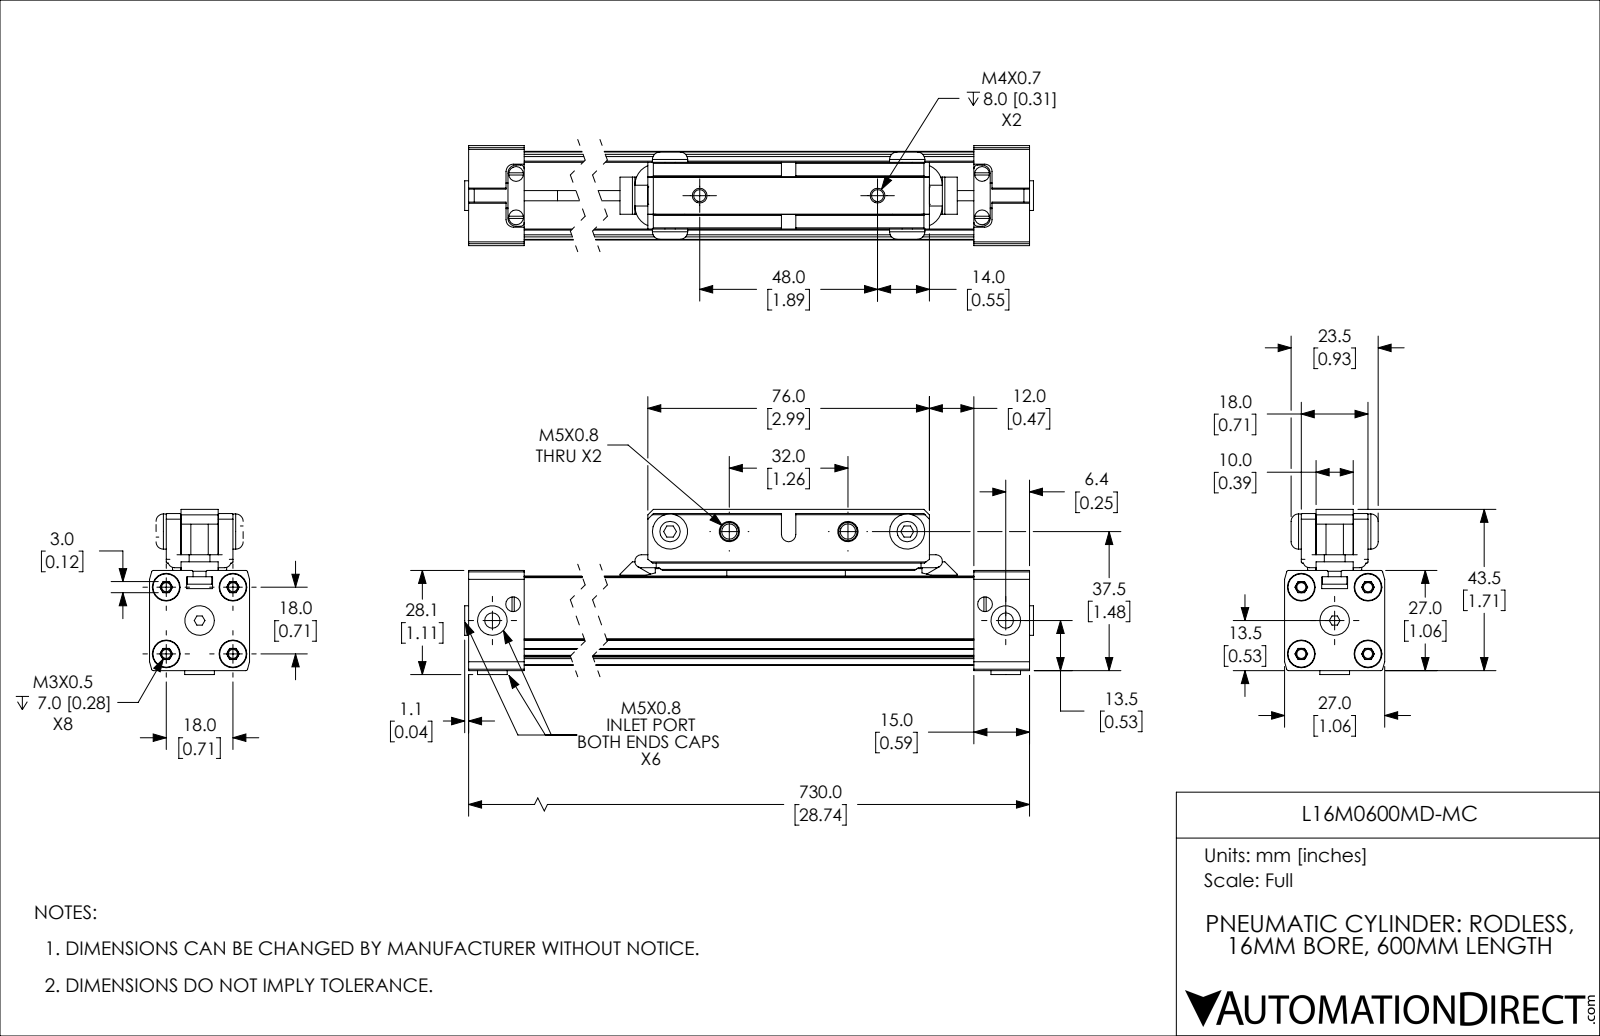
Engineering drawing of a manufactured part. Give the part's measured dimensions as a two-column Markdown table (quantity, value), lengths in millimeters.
| quantity | value |
| --- | --- |
| part name | L16M0600MD-MC; L16M0600MD-MC_BODY; L16M0600MD-MC_PISTON |
| STEP written by | SolidWorks 2019 (CONFIG_CONTROL_DESIGN) |
| units | millimeters |
| bodies | 13 solids, 827 faces (435 planar, 284 cylindrical, 108 other) |
| overall size | 732.15 × 44.57 × 27 |
| volume | 290 406 mm³ |
| surface area | 150 391 mm² |
| round holes (diameter × count) | 4.13 × 9, 4 × 6, 8 × 5, 2.46 × 4, 5.5 × 4, 7.5 × 4, 3.24 × 2, 16.1 × 1 |
| round bosses / shafts (diameter × count) | 7.2 × 4, 3.5 × 4, 5 × 3, 3.8 × 3, 9.5 × 2, 16 × 1 |
| partial cylindrical surfaces (radius × count) | 0.3 × 22, 0.5 × 14, 0.25 × 8, 0.62 × 6, 1 × 6, 0.2 × 4, 0.6 × 4, 2 × 4 |
| main face-to-face distances | 23.9, 24, 10.58, 13.32, 20.95, 2.74, 2.95, 7.63, 10.37, 1.5 |
| hole center spacings | 8.67, 12.73, 18, 710.82, 48, 7.12, 11.7, 11.91 |
